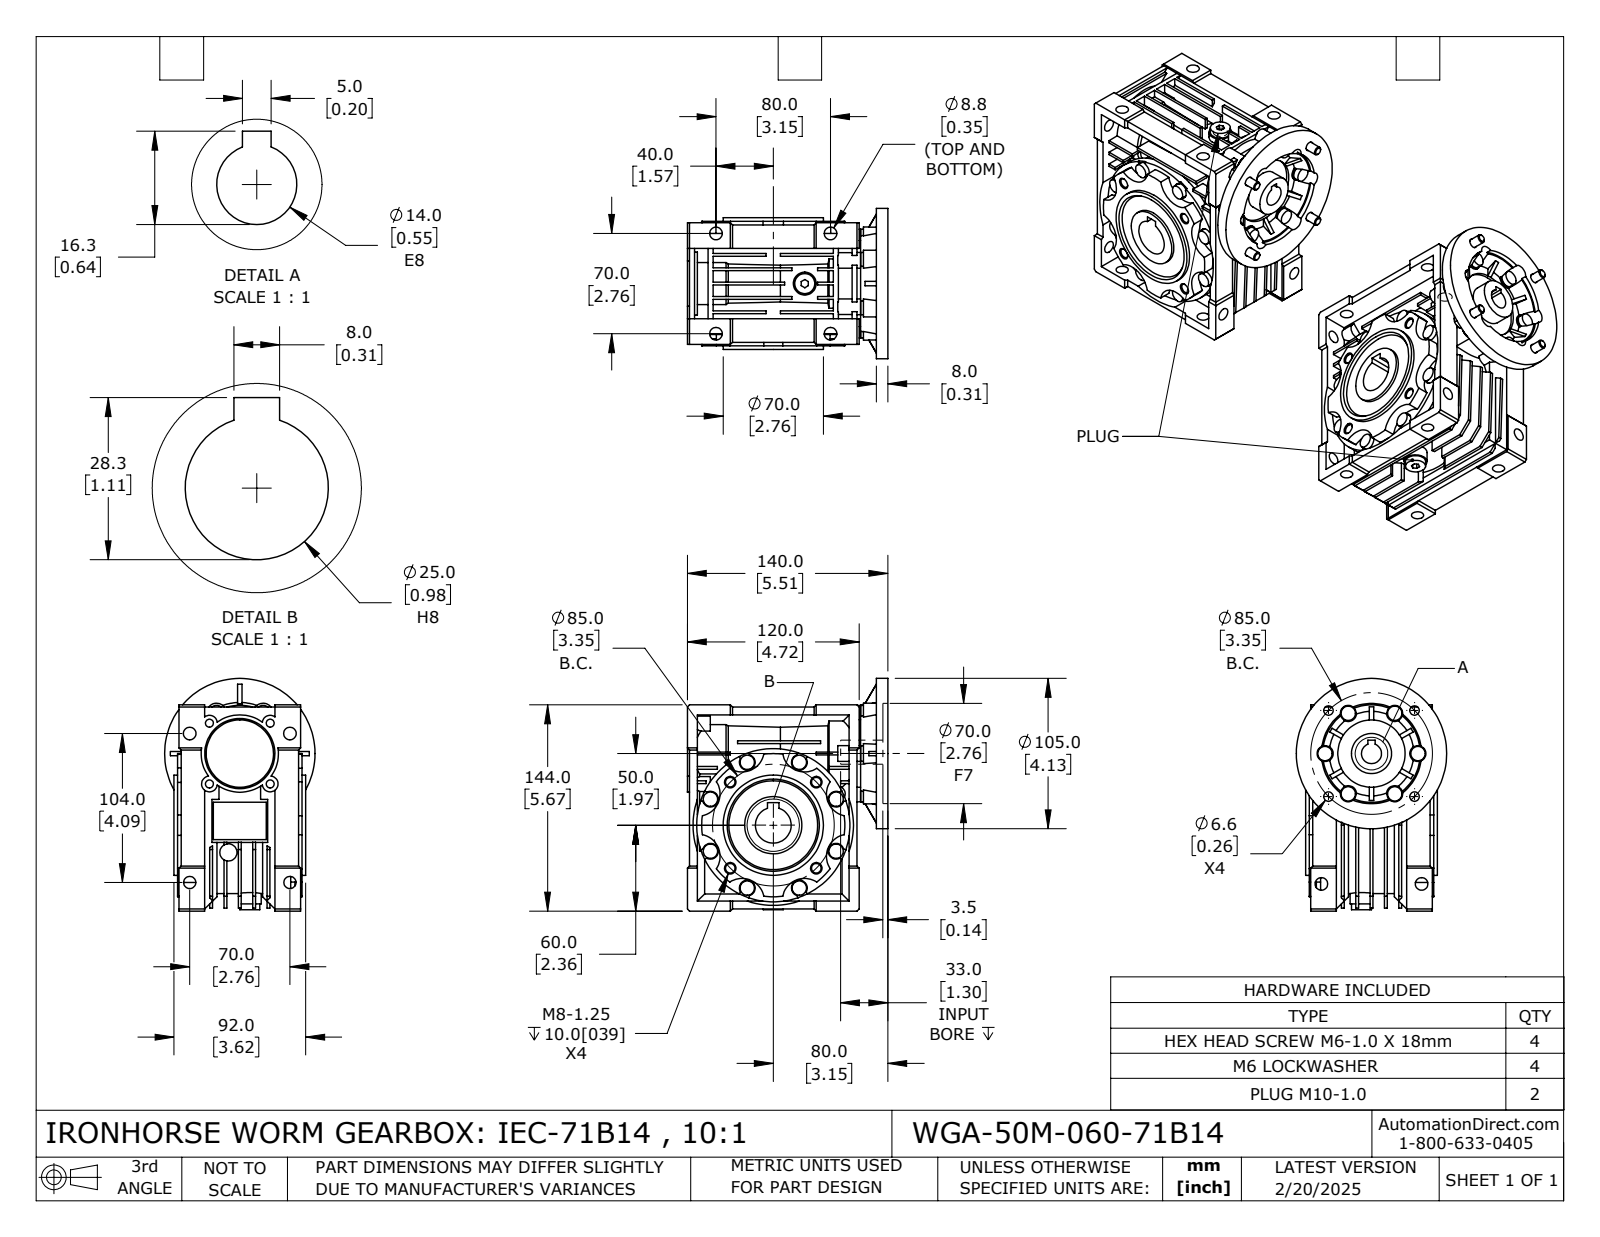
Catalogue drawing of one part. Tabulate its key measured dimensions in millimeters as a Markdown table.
| quantity | value |
| --- | --- |
| part name | WGA-50M-060-71B14 |
| STEP written by | SolidWorks 2024 (CONFIG_CONTROL_DESIGN) |
| units | millimeters |
| bodies | 15 solids, 1132 faces (615 planar, 372 cylindrical, 145 other) |
| overall size | 162.5 × 148.5 × 105 |
| volume | 1 065 000 mm³ |
| surface area | 235 209 mm² |
| round holes (diameter × count) | 8.8 × 8, 8.5 × 6, 5.55 × 4, 6.1 × 4, 6.6 × 4, 6.65 × 2, 6.65 × 2, 9 × 2, 14 × 1, 15 × 1, 25 × 1, 28 × 1 |
| round bosses / shafts (diameter × count) | 10 × 14, 12.2 × 4, 6 × 4, 16 × 2, 14 × 2, 9.8 × 2, 8.3 × 2, 107 × 1 |
| partial cylindrical surfaces (radius × count) | 5.5 × 18, 6 × 8, 15 × 8, 15.5 × 8, 5.75 × 6, 7 × 6, 20.76 × 1, 35 × 1 |
| main face-to-face distances | 8, 2, 10, 7, 1.5, 5.5, 20, 12, 55, 35 |
| hole center spacings | 42.5, 52.02, 60.1, 70, 12.5, 30, 42.42, 72.49 |
